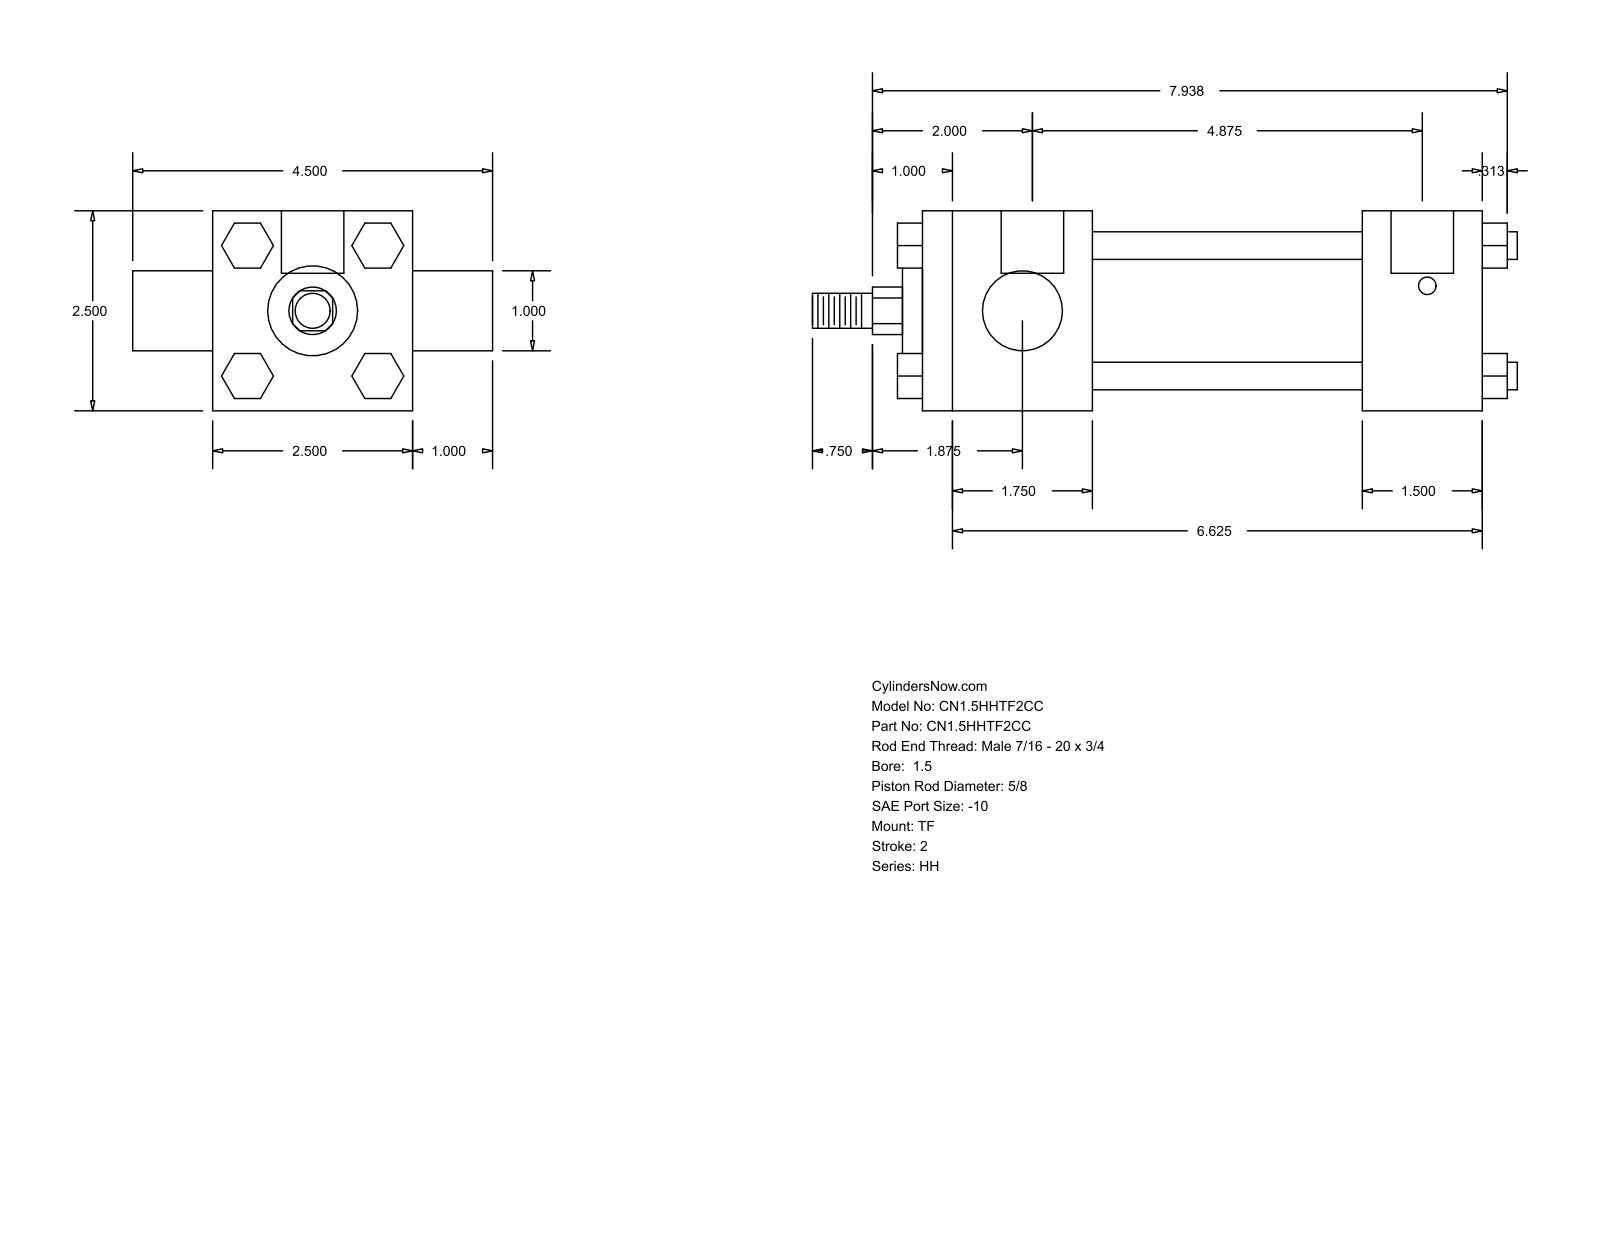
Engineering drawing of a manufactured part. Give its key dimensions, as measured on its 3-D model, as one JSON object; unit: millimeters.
{"part_name": "HH_TF__0150_0.625", "step_written_by": "GSSL Pune (CONFIG_CONTROL_DESIGN)", "units": "millimeters", "bodies": {"solids": 0, "faces": 120, "planar": 92, "cylindrical": 28, "other": 0}, "overall_size": [223.84, 114.3, 63.5], "round_holes": [[5.56, 3], [19.84, 2]], "round_bosses_or_shafts": [[8.76, 4], [44.45, 1], [28.57, 1], [25.4, 1], [15.88, 1], [11.11, 1]], "partial_cylinders_radius": [[7.54, 1]], "face_to_face_distances": [63.5, 177.8, 53.97, 123.83, 139.69, 85.72, 38.11, 25.4, 88.9, 20.7], "hole_center_spacings": [1.59, 125.41, 123.82, 127]}
